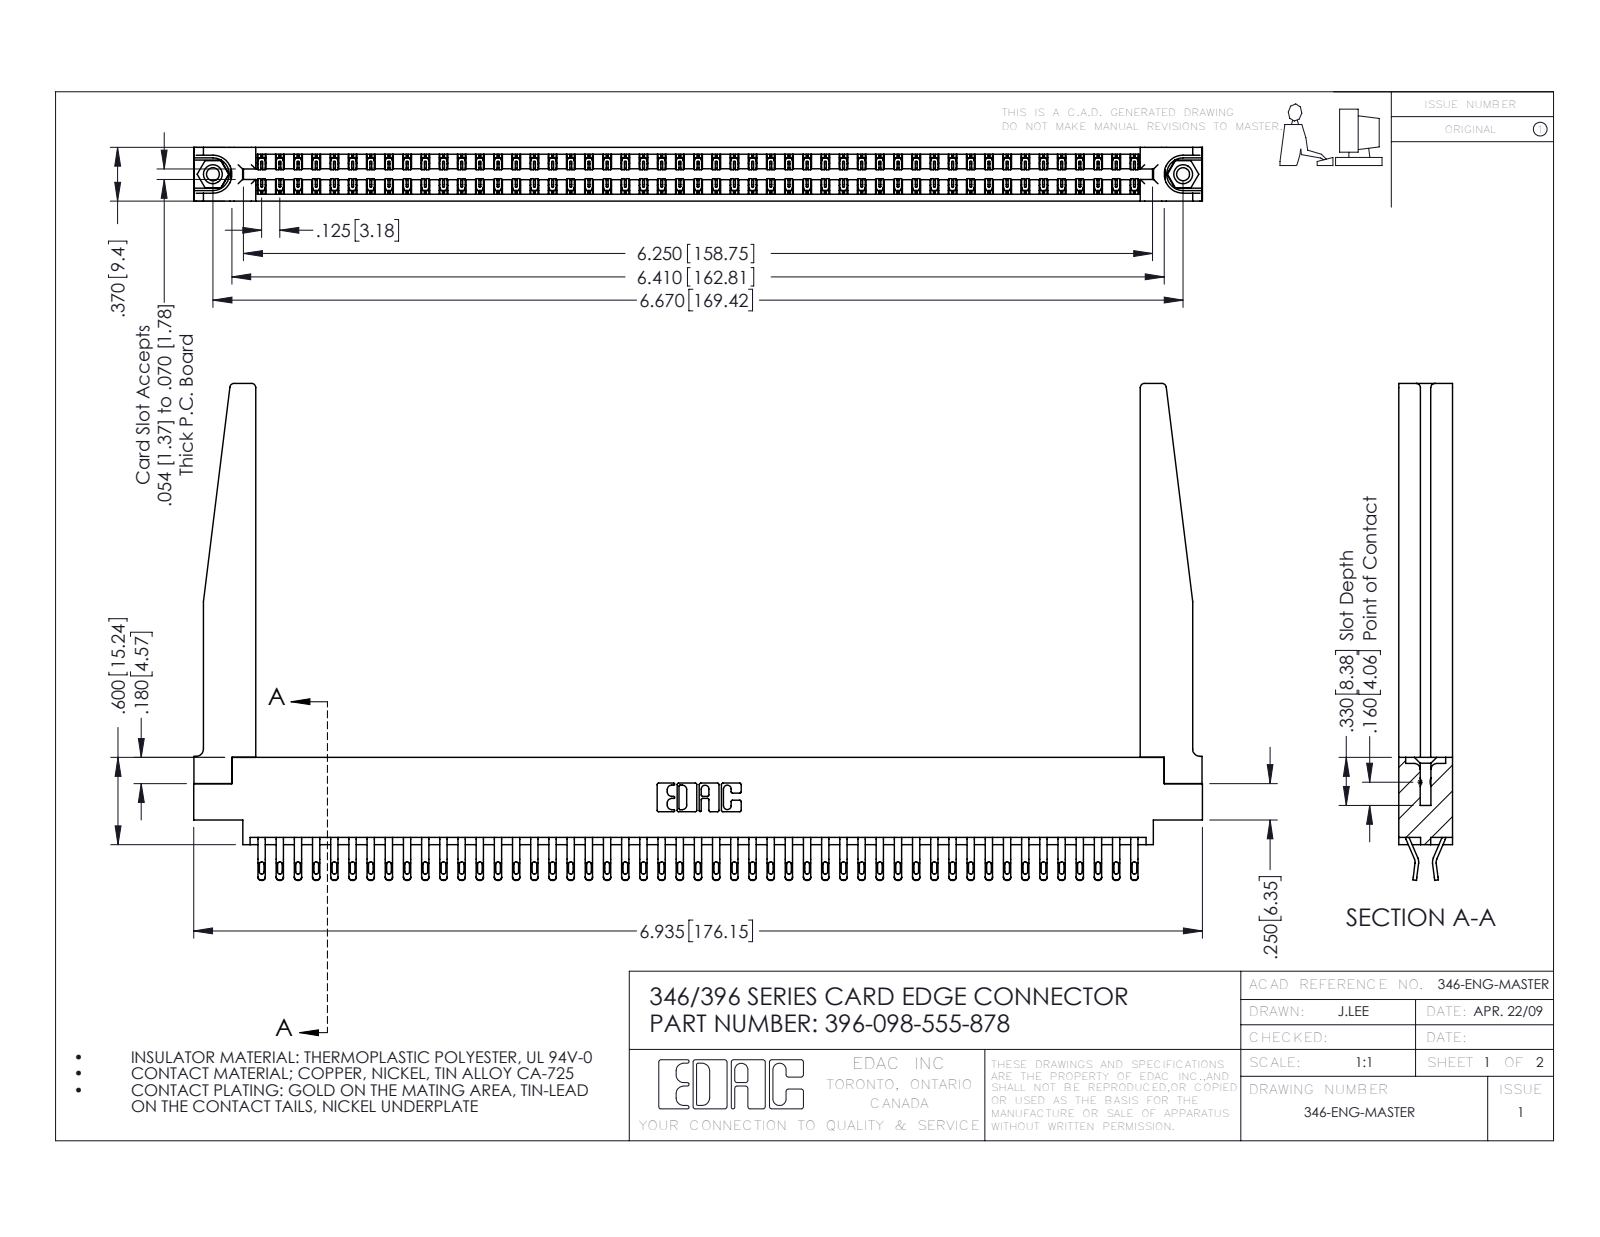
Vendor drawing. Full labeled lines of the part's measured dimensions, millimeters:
Part name (STEP PRODUCT): 396-098-555-878; 346 Part_0.170 Offset - 0.156 Dia-TH; 346-220-078_345-220-078; 345-250-001_345-250-001-102 (+1 more)
STEP written by: SolidWorks 2016 (CONFIG_CONTROL_DESIGN)
Units: millimetres
Bodies: 103 solids, 6044 faces (3456 planar, 2536 cylindrical, 52 other)
Overall size (bounding box): 176.1 × 86.7 × 9.4
Volume: 24 270 mm³ · Surface area: 31 700 mm²
Round holes (diameter × count): ⌀2.3 ×2, ⌀3.2 ×2, ⌀4 ×2, ⌀1.6 ×1
Round bosses / shafts (diameter × count): ⌀3.9 ×2
Partial cylindrical surfaces — rounded edges, fillets, slot ends (radius × count): R0.4 ×196, R0.5 ×196, R0.2 ×147, R0.3 ×22, R0.8 ×8, R0.2 ×6, R0.8 ×6, R1.3 ×4
Main face-to-face distances: 9.4, 1.2, 8.2, 1.8, 3.8, 3.8, 6.4, 0.6, 7.6, 7
Hole centre spacings: 6.2, 164.1, 169.4
